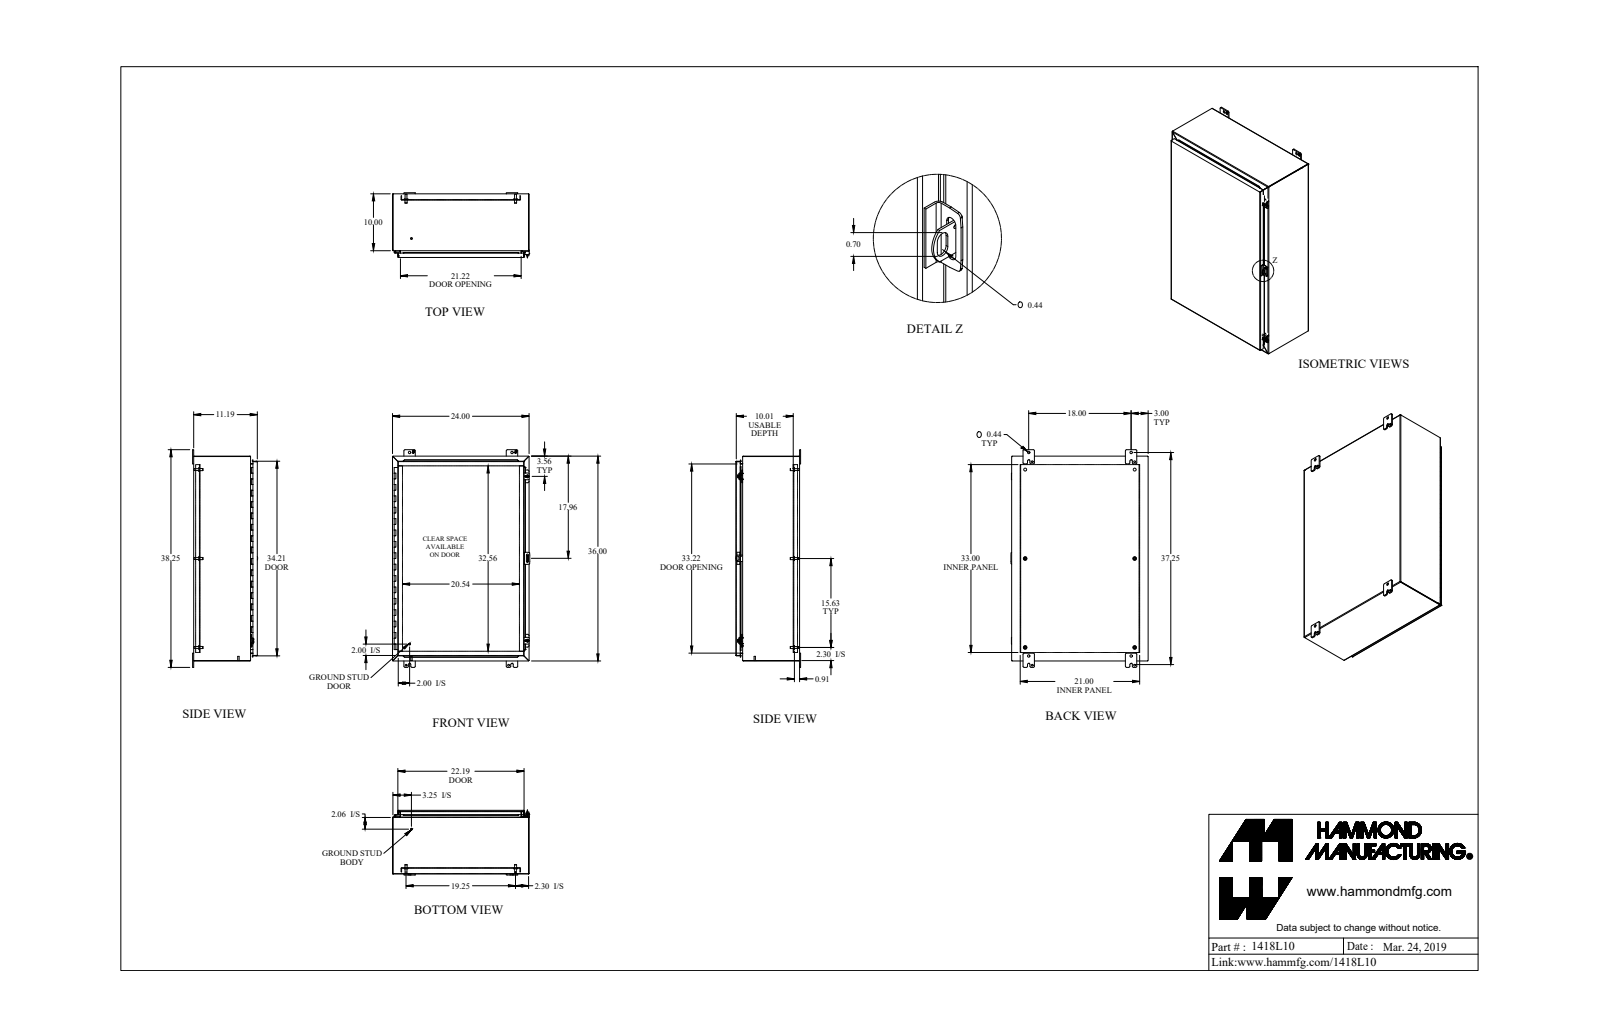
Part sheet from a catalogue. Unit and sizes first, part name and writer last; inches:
Units: inches
Overall size (bounding box): 38.25 × 24.125 × 11.437
Round holes (diameter × count): ⌀0.5 ×6, ⌀0.307 ×4, ⌀0.313 ×4, ⌀0.437 ×4, ⌀0.213 ×2, ⌀0.265 ×2, ⌀0.375 ×2, ⌀0.445 ×2, ⌀0.445 ×2, ⌀0.125 ×1, ⌀0.187 ×1
Round bosses / shafts (diameter × count): ⌀0.65 ×6, ⌀0.375 ×6, ⌀0.33 ×6, ⌀1 ×4, ⌀0.5 ×2, ⌀0.39 ×2, ⌀0.281 ×2, ⌀0.25 ×2
Partial cylindrical surfaces — rounded edges, fillets, slot ends (radius × count): R0.188 ×26, R0.036 ×24, R0.108 ×24, R0.048 ×13, R0.143 ×13, R0.045 ×8, R0.218 ×8, R0.25 ×8
Main face-to-face distances: 0.072, 11.113, 11.041, 0.937, 11.185, 0.095, 1.009, 23.928, 10.081, 10.009
Hole centre spacings: 19.25, 15.625, 24.793, 18, 31.25, 36.703, 40.026, 2.434
Volume: 326.4 in³ · Surface area: 8 471 in²
Bodies: 44 solids, 1333 faces (791 planar, 458 cylindrical, 84 other)
Part name (STEP PRODUCT): 1418L10_Default
STEP written by: SolidWorks 2019 (CONFIG_CONTROL_DESIGN)
